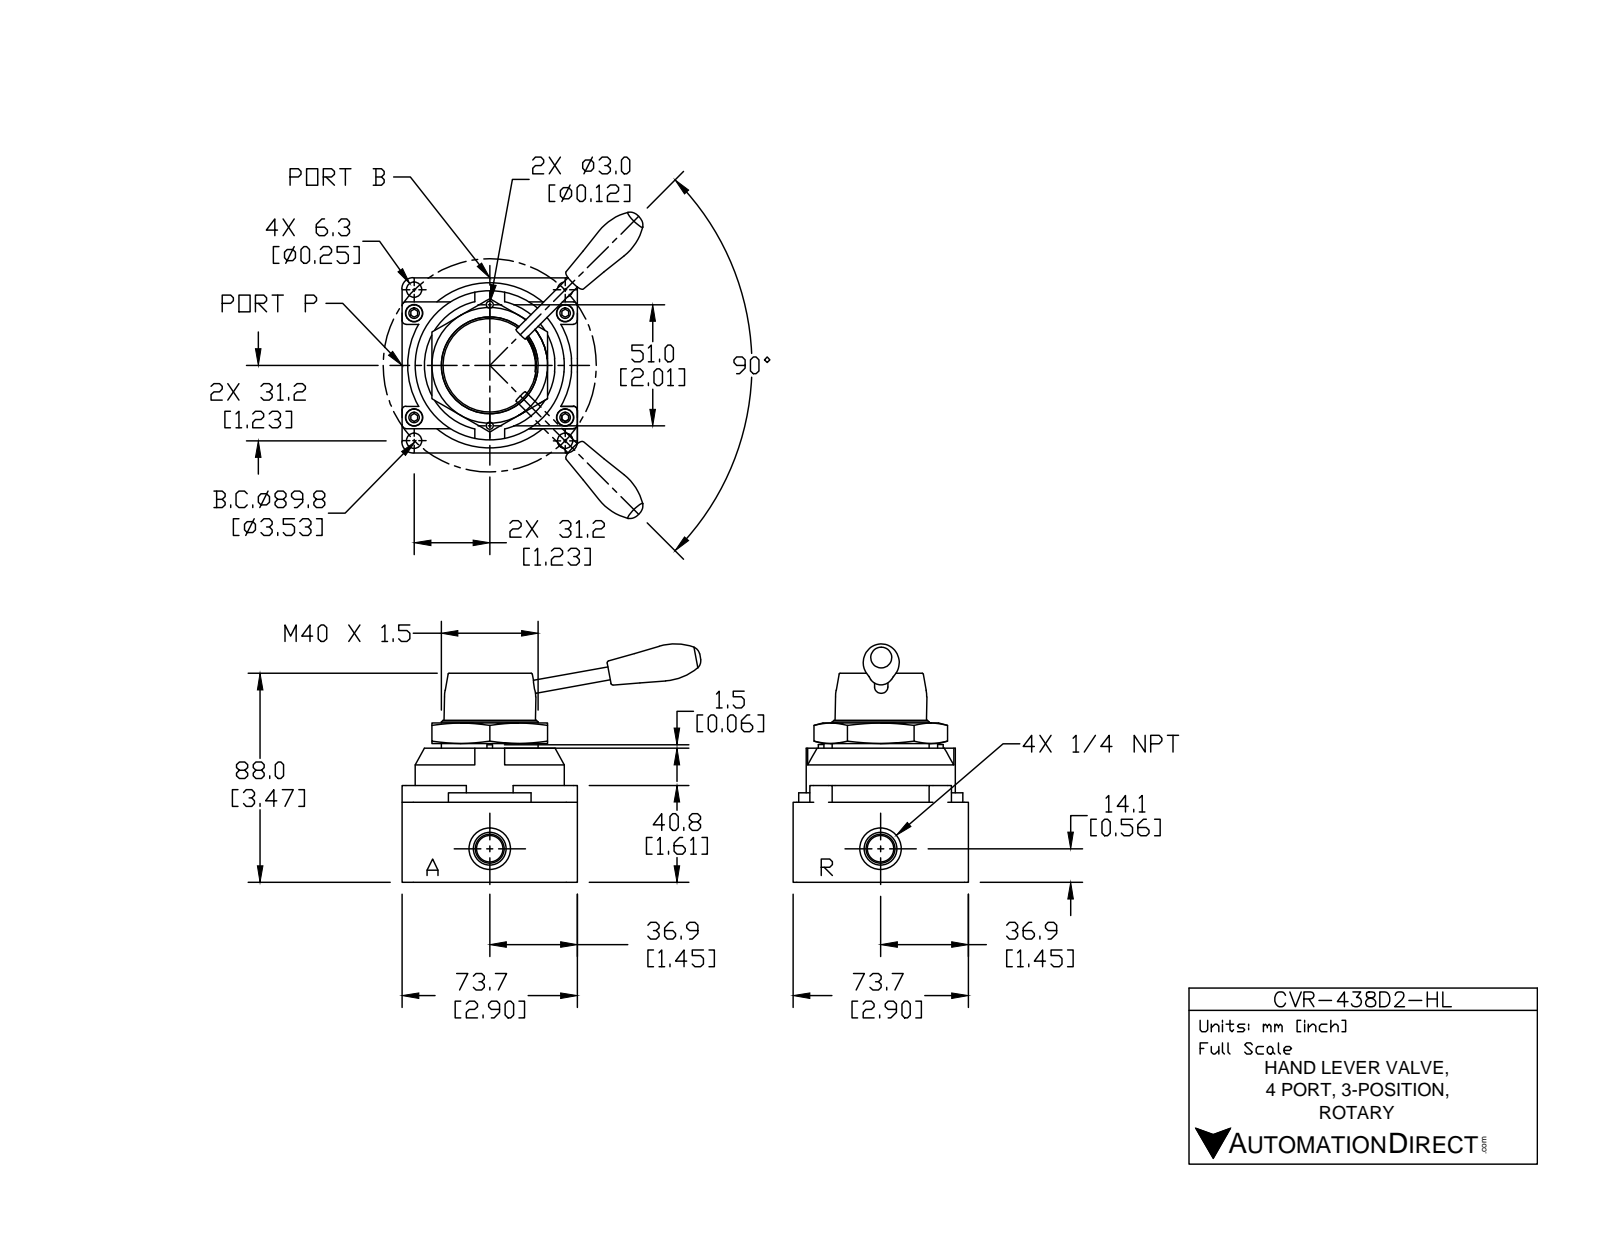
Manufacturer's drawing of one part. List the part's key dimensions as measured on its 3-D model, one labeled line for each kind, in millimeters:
Part name (STEP PRODUCT): CVR-438D2-HL
STEP written by: SolidWorks 2015 (CONFIG_CONTROL_DESIGN)
Units: millimetres
Bodies: 3 solids, 221 faces (86 planar, 71 cylindrical, 64 other)
Overall size (bounding box): 140 × 104 × 74
Volume: 275 300 mm³ · Surface area: 50 230 mm²
Round holes (diameter × count): ⌀6.6 ×4, ⌀9.2 ×4, ⌀17.8 ×2, ⌀20 ×1, ⌀33 ×1
Round bosses / shafts (diameter × count): ⌀9 ×4, ⌀3 ×2, ⌀58 ×1, ⌀40 ×1, ⌀34.5 ×1, ⌀20 ×1, ⌀7.1 ×1
Partial cylindrical surfaces — rounded edges, fillets, slot ends (radius × count): R2 ×8, R1 ×4, R6 ×4, R33 ×1
Main face-to-face distances: 74, 71, 27, 44, 12, 17.5, 52.5, 13, 36, 18.5
Hole centre spacings: 62, 13, 35.8, 43.8, 49, 63.3, 79, 36
